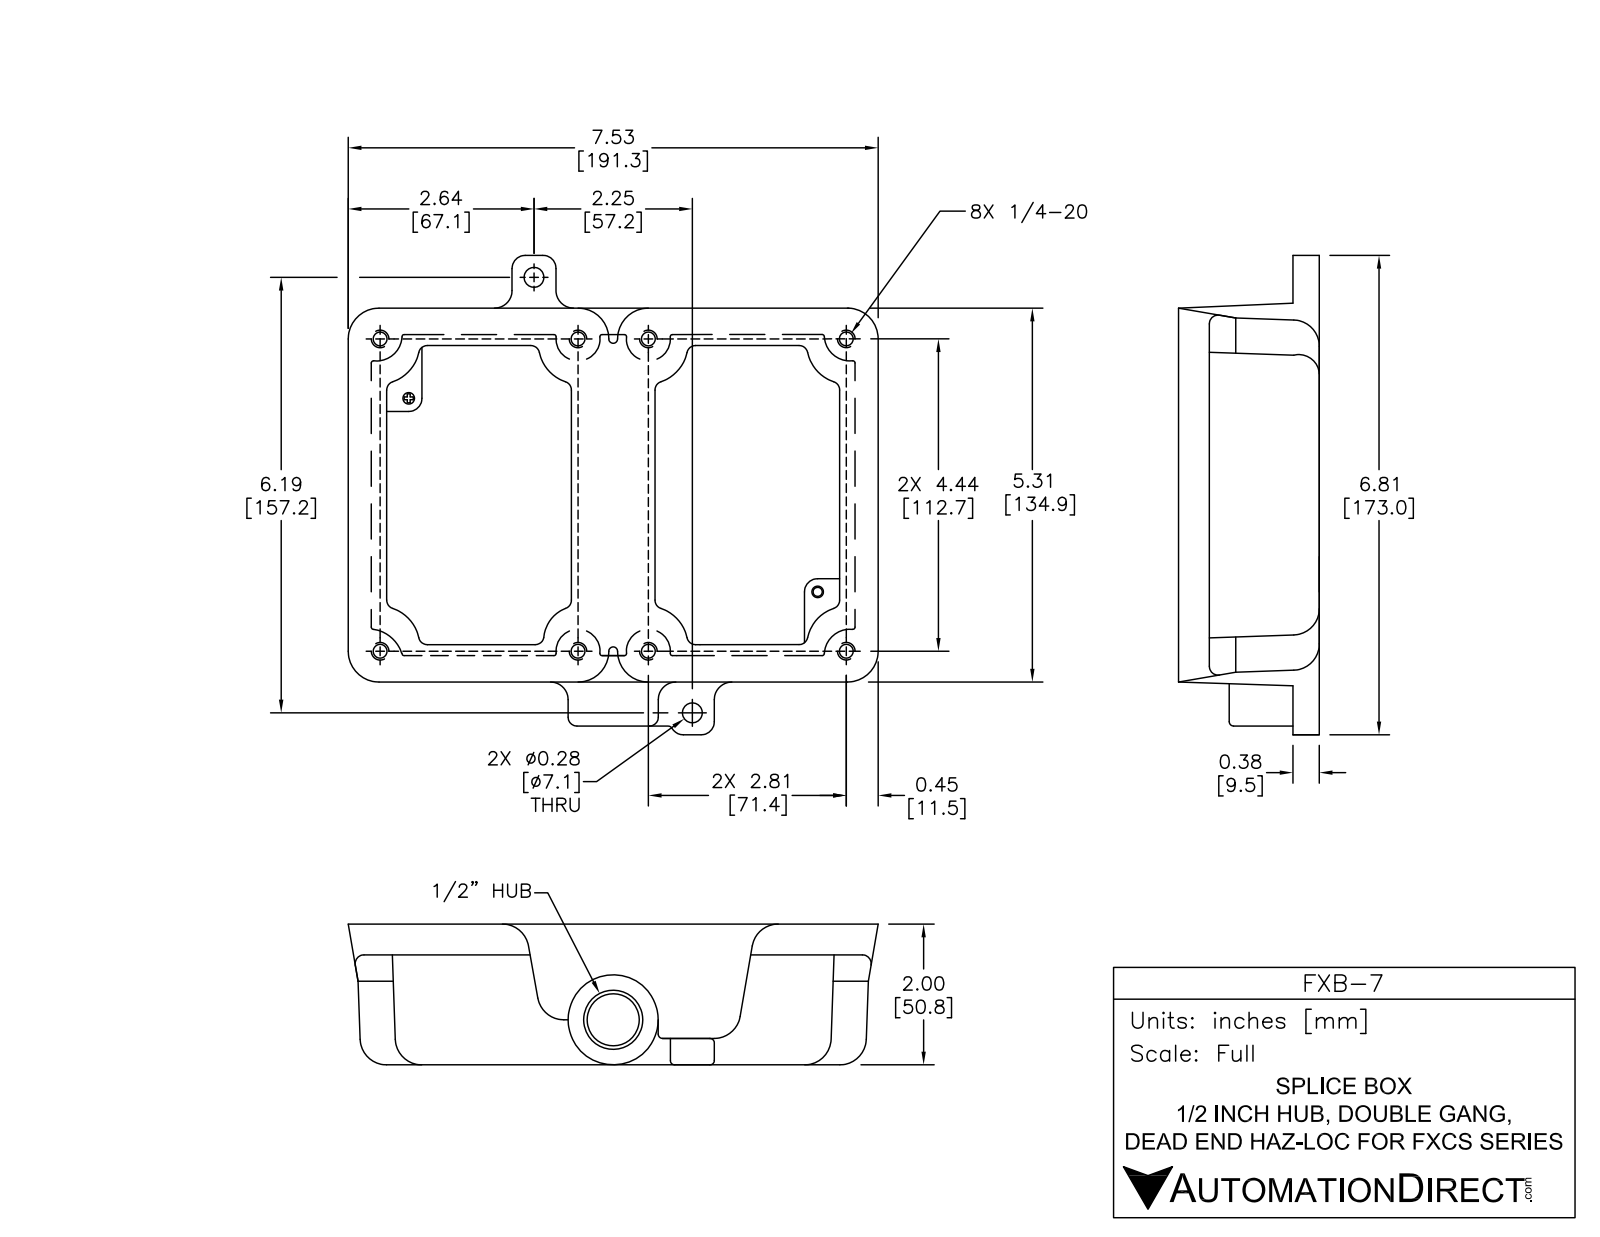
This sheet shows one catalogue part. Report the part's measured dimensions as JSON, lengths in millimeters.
{"part_name": "FXB-7", "step_written_by": "SolidWorks 2015 (AUTOMOTIVE_DESIGN)", "units": "millimeters", "bodies": {"solids": 3, "faces": 382, "planar": 155, "cylindrical": 135, "other": 92}, "overall_size": [191.5, 174, 52.25], "volume_mm3": 464867, "surface_area_mm2": 118370, "round_holes": [[5, 8], [7, 2], [14, 1], [18.25, 1]], "round_bosses_or_shafts": [[8, 2], [12.2, 1]], "partial_cylinders_radius": [[3, 36], [4.5, 16], [9, 8], [12.75, 8], [2, 7], [4, 6], [6, 4], [7.1, 3]], "face_to_face_distances": [7.5, 44.75, 52.25, 14.13, 121.87, 107.74, 136, 12.75, 32, 39.5], "hole_center_spacings": [95.75, 112.5, 133.3, 71.49, 71.51, 115.08, 136.04, 146.72]}
